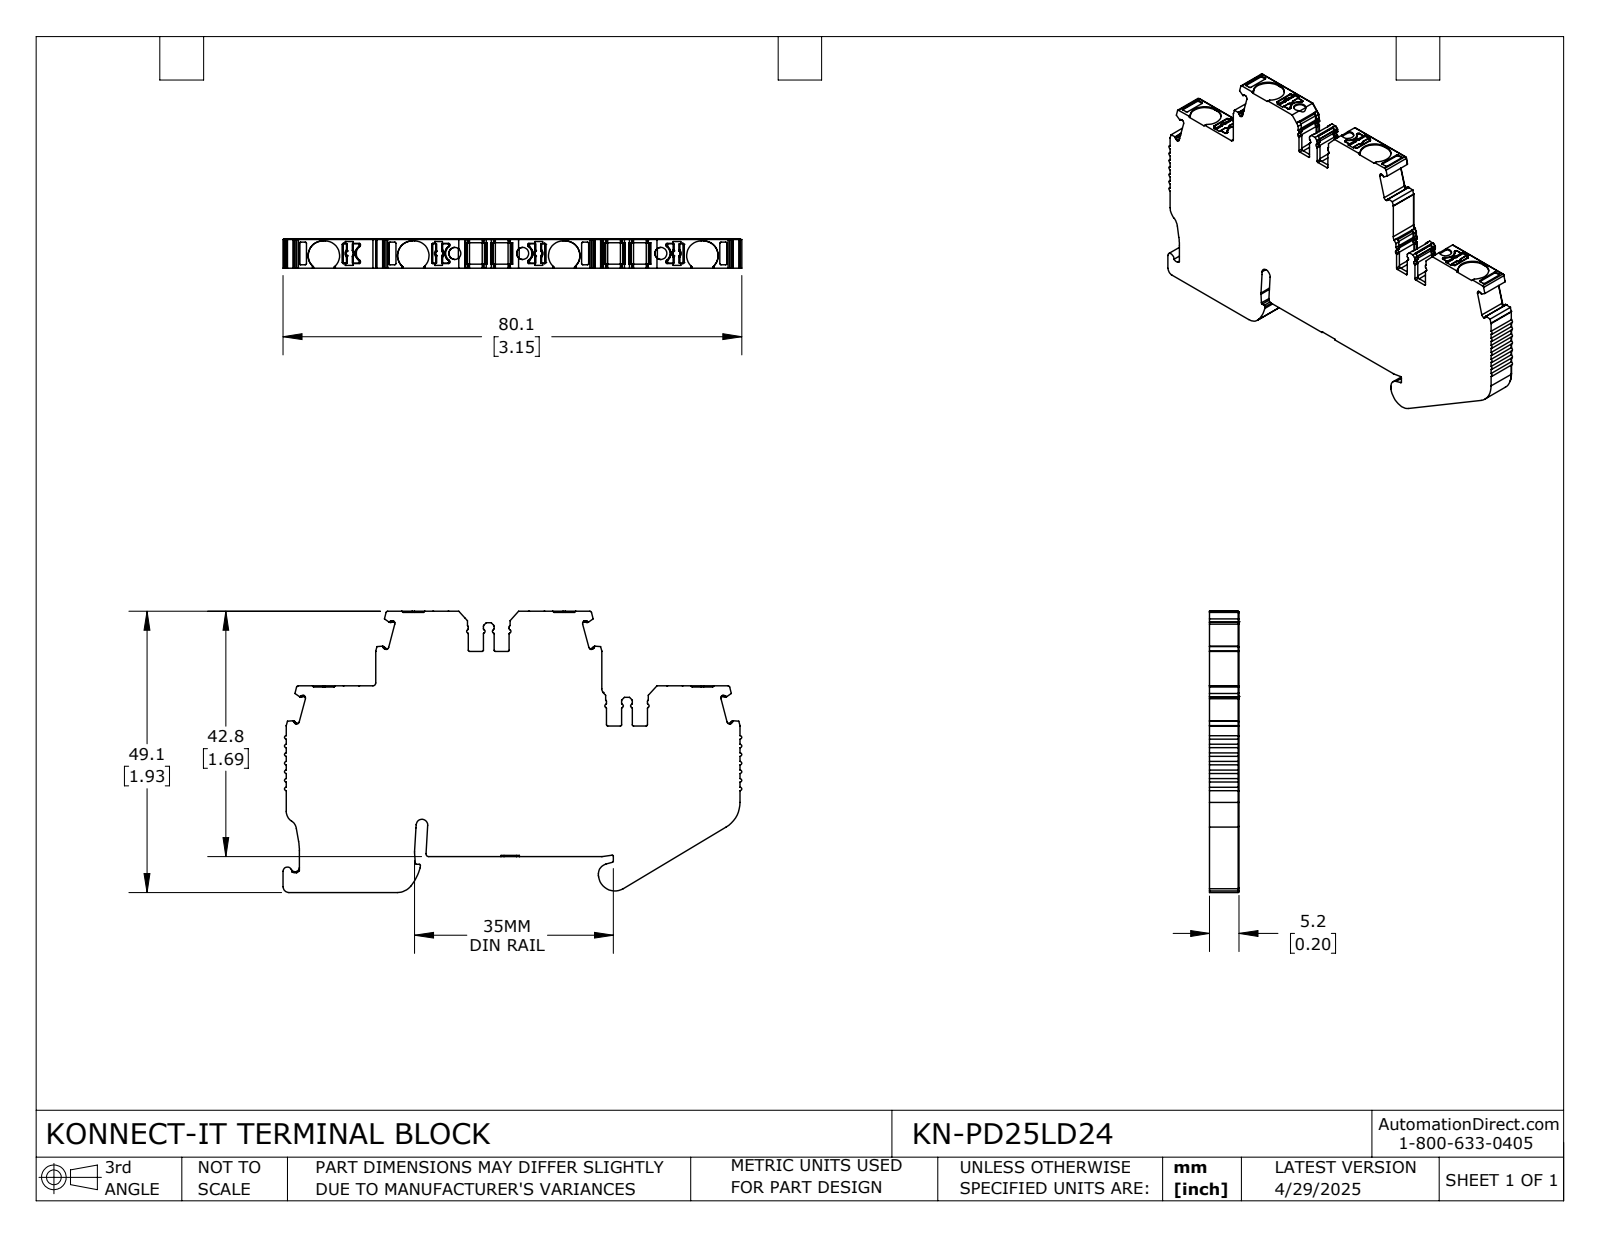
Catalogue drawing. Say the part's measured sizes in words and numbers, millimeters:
The part is named "KN-PD25LD24". Its 3-D file was written by "SolidWorks 2024 (CONFIG_CONTROL_DESIGN)". It is 1 solid with 979 faces: 470 planar, 438 cylindrical and 71 other. Overall it measures 80.1 by 49.1 by 5.2 millimeters. Its volume is 14 600 cubic millimeters and its surface area 7 503 square millimeters. Round holes: 3 of diameter 2.1. Partial cylindrical surfaces (rounded edges, fillets, slot ends): 100 of radius 0.2, 57 of radius 0.3, 41 of radius 0.1, 21 of radius 0.5, 17 of radius 0.4, 16 of radius 0.2, 9 of radius 0.6, 8 of radius 0.2. The main face-to-face distances are 5.2, 13, 6.2, 42.6, 29.6, 48.9, 2, 35.9, 12.8, 24.1. The hole center spacings are 11.8, 24.1, 36.
